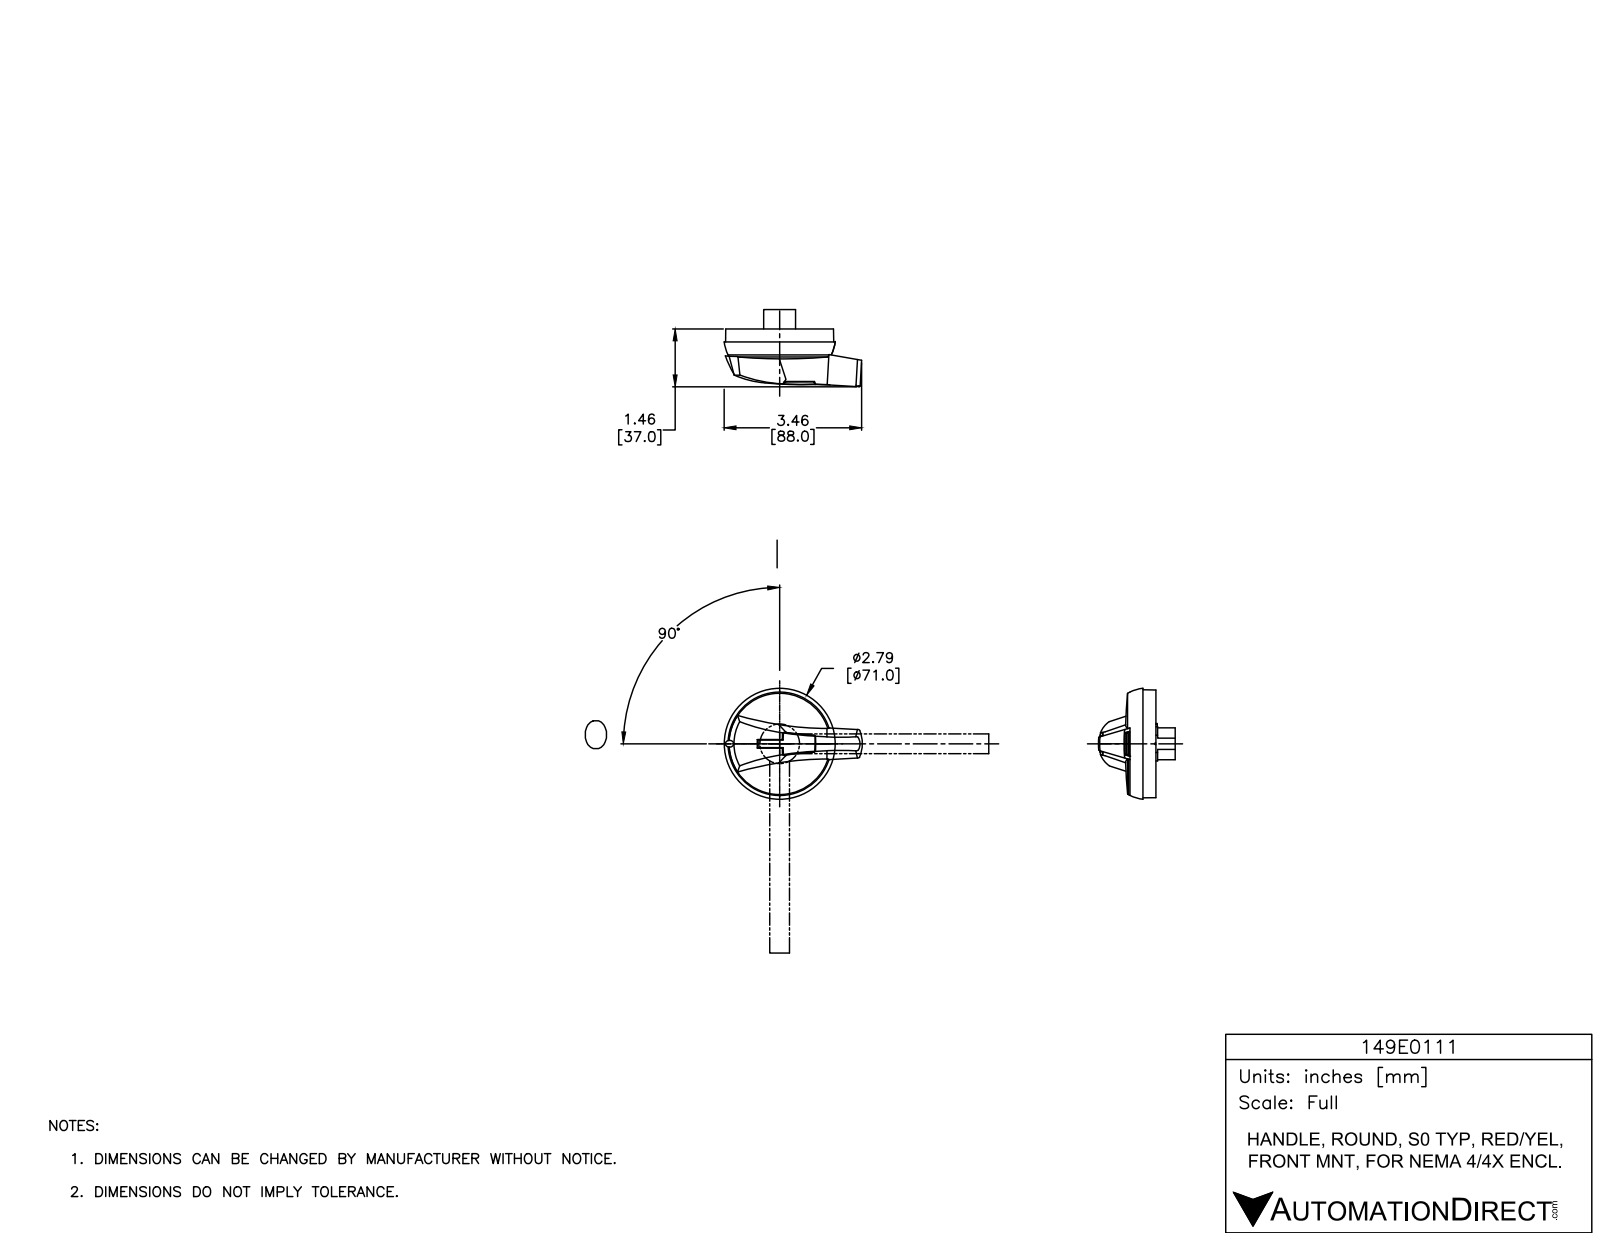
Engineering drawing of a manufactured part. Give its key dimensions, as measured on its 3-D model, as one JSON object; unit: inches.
{"part_name": "149E0111", "step_written_by": "SolidWorks 2015 (AUTOMOTIVE_DESIGN)", "units": "inches", "bodies": {"solids": 6, "faces": 2118, "planar": 468, "cylindrical": 373, "other": 1277}, "overall_size": [3.479, 2.8, 1.925], "volume_in3": 3.457, "surface_area_in2": 93.25, "round_holes": [[0.169, 4], [0.193, 4], [0.394, 4], [0.079, 3], [0.13, 2], [0.157, 2], [0.335, 2], [0.118, 1], [0.126, 1], [0.457, 1], [0.89, 1], [2.618, 1]], "round_bosses_or_shafts": [[2.559, 1], [0.984, 1]], "partial_cylinders_radius": [[0.02, 114], [0.039, 23], [0.01, 19], [0.012, 10], [0.03, 8], [0.641, 6], [0.142, 4], [0.187, 4]], "face_to_face_distances": [0.059, 0.071, 0.13, 0.616, 0.053, 0.03, 0.557, 0.486, 0.152, 0.295], "hole_center_spacings": [0.564, 0.961, 1.557, 0.669, 0.677, 1.102, 1.181, 1.575]}
